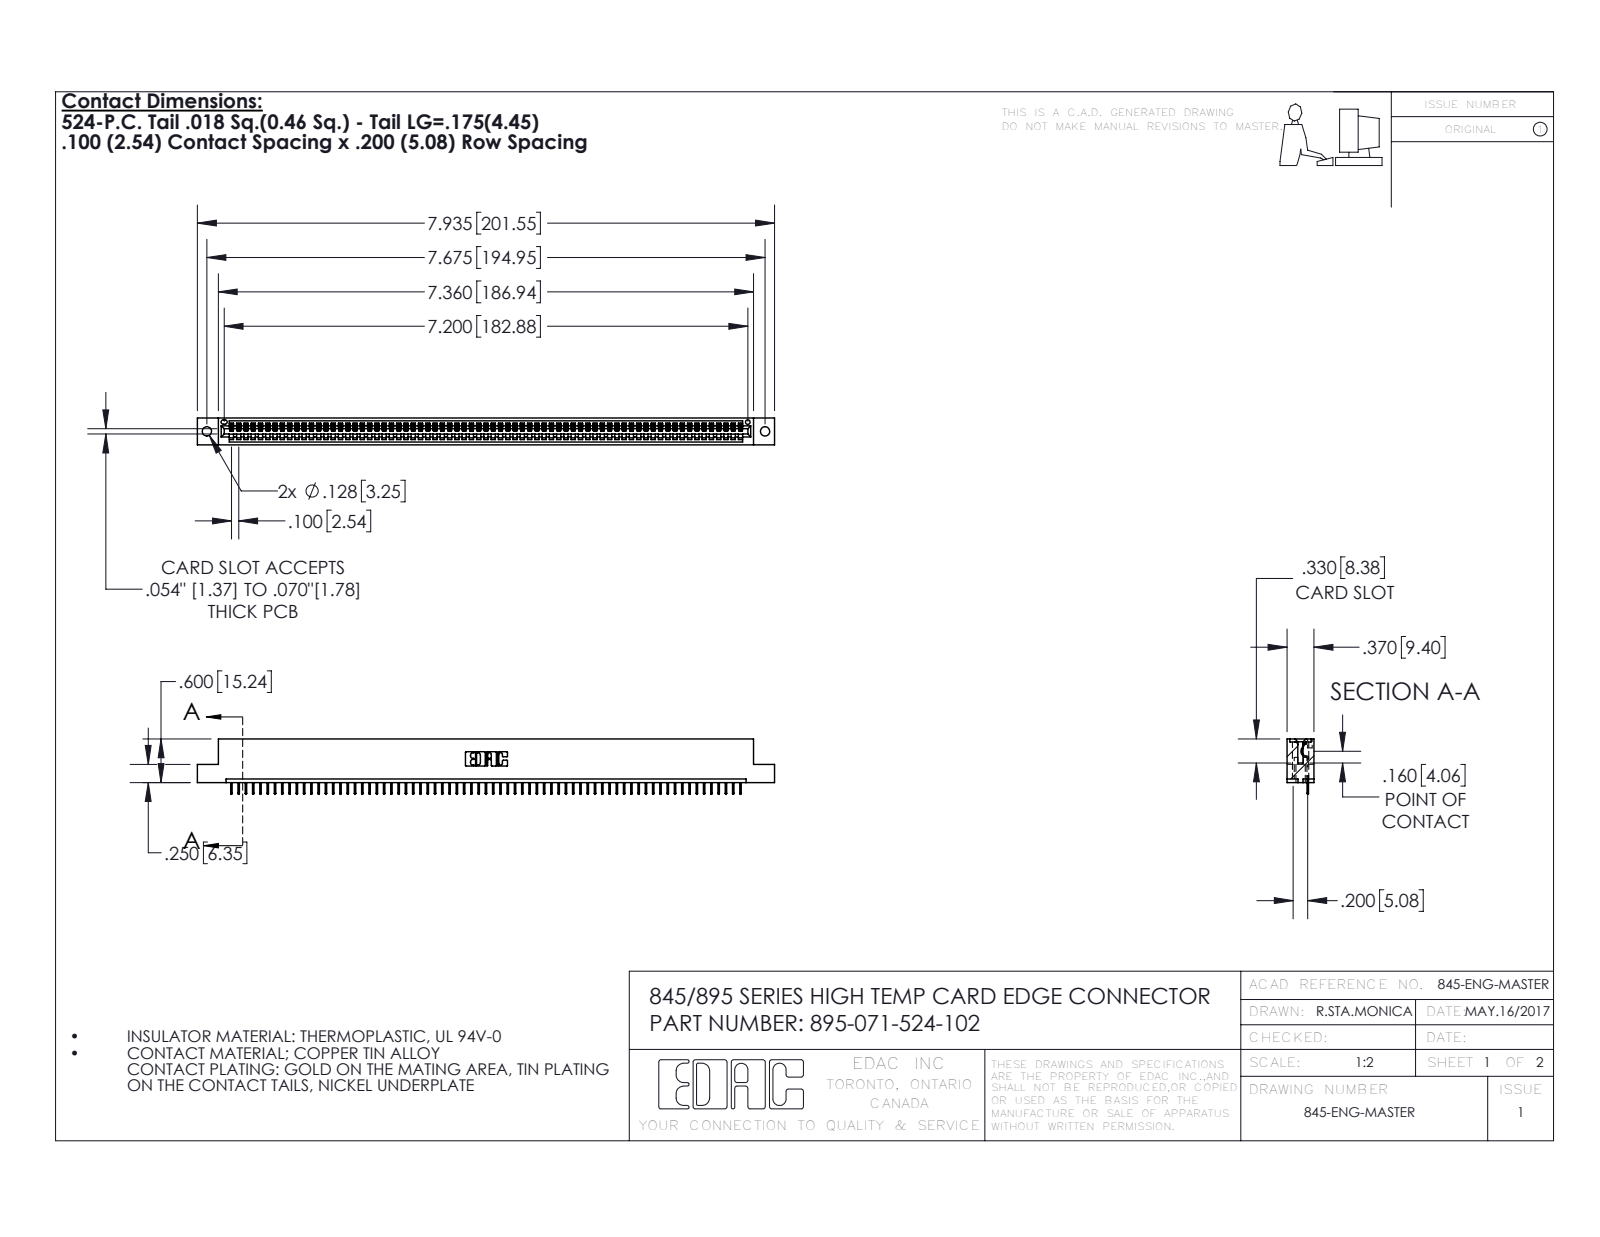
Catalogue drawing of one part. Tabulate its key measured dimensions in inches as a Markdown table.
| quantity | value |
| --- | --- |
| part name | 345-292-001_345-293-124; 395-071-524-102; 345 Part_Flush Mounting Lugs - 0.128 Dia |
| STEP written by | SolidWorks 2016 (CONFIG_CONTROL_DESIGN) |
| units | inches |
| bodies | 38 solids, 2964 faces (2258 planar, 706 cylindrical, 0 other) |
| overall size | 7.935 × 0.762 × 0.37 |
| volume | 1.148 in³ |
| surface area | 35 in² |
| round holes (diameter × count) | 0.128 × 2, 0.064 × 1 |
| partial cylindrical surfaces (radius × count) | 0.006 × 74, 0.01 × 22, 0.007 × 6, 0.031 × 6, 0.026 × 3, 0.031 × 2, 0.04 × 2, 0.014 × 1 |
| main face-to-face distances | 0.298, 0.072, 0.37, 0.2, 0.098, 0.272, 0.025, 0.225, 0.072, 0.149 |
| hole center spacings | 0.27, 7.439, 7.675 |
